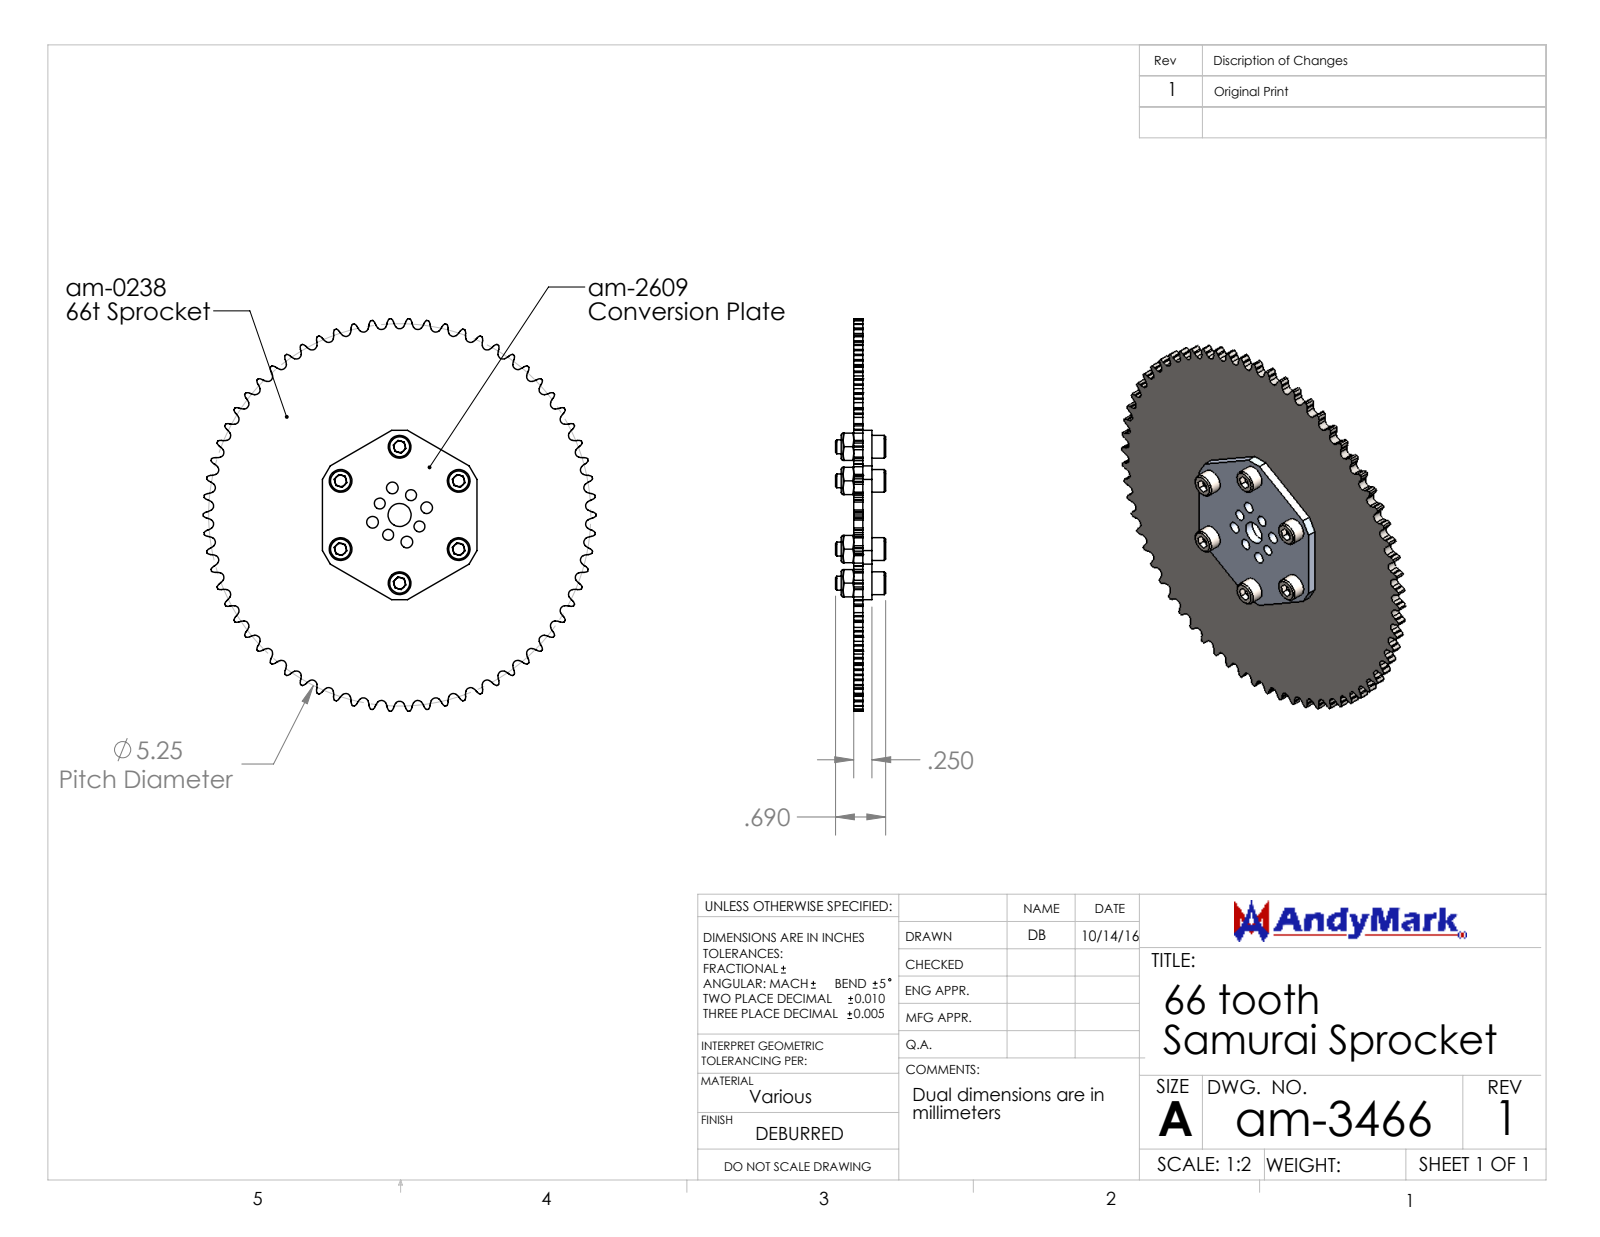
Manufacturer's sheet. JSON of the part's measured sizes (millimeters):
{"part_name": "FTC Conversion Plate REV 2; 10-32x0500_shcs_HX-SHCS 0.19-32x1.375x1-C; am-3466 66t Samurai Sprocket; 10-32 Nylock Jam Nut_90633A411 (+1 more)", "step_written_by": "SolidWorks 2014 (AUTOMOTIVE_DESIGN)", "units": "millimeters", "bodies": {"solids": 20, "faces": 1275, "planar": 310, "cylindrical": 647, "other": 318}, "overall_size": [137.1, 137, 17.5], "volume_mm3": 52880, "surface_area_mm2": 40520, "round_holes": [[4.2, 24], [4.1, 6], [4.8, 6], [5.1, 6], [5.3, 6], [6.1, 6], [3.8, 4], [4.1, 4], [8.1, 1], [28.6, 1]], "round_bosses_or_shafts": [[8, 6]], "partial_cylinders_radius": [[2.6, 132], [4.3, 132], [1.7, 66], [2.1, 6], [68.6, 1]], "face_to_face_distances": [3.2, 6.4, 3.2, 0.5, 3.7, 6.9, 10.1, 3.6, 6.8, 10], "hole_center_spacings": [23.8, 47.6, 41.1, 41.2, 23.6, 23.7, 41.2, 23.8]}
